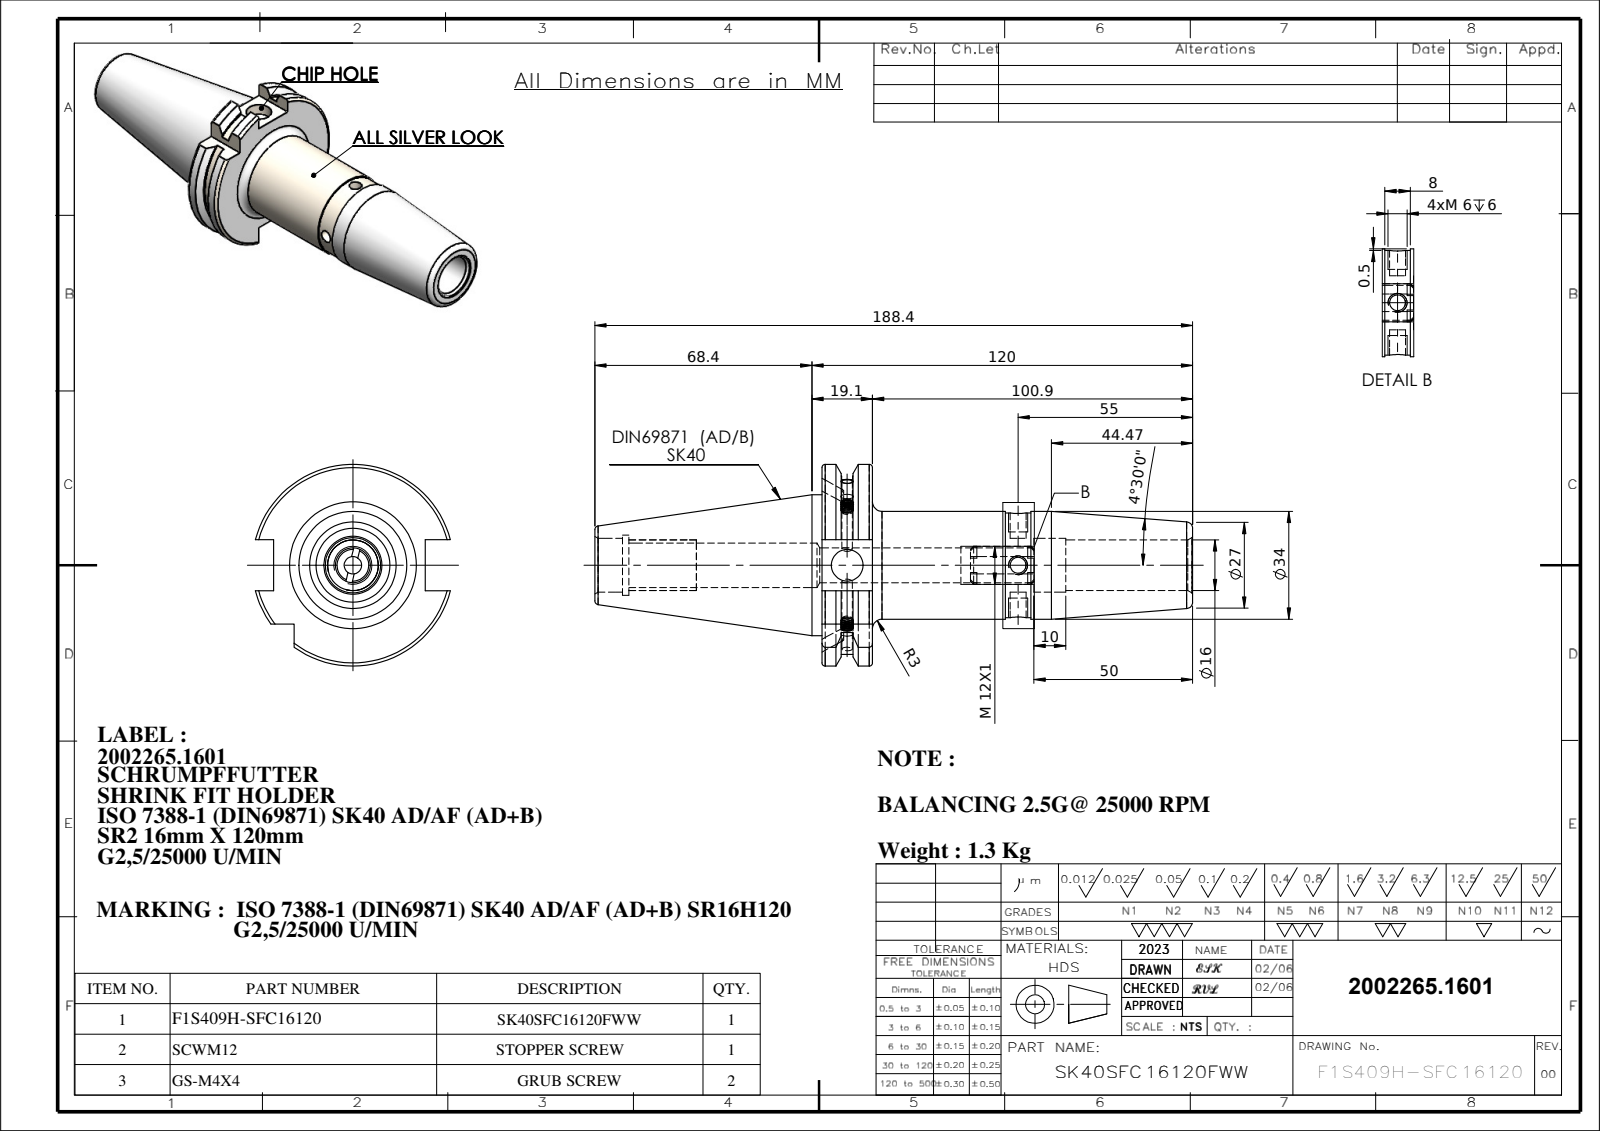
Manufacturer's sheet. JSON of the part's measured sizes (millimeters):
{"part_name": "GS-M4X4_DIN 913 - M4 x 4-N; 91406-SR216120; SCWM12; SK40SFC16120FWW", "step_written_by": "SolidWorks 2018 (CONFIG_CONTROL_DESIGN)", "units": "millimeters", "bodies": {"solids": 4, "faces": 238, "planar": 70, "cylindrical": 70, "other": 98}, "overall_size": [188.4, 63.55, 61.48], "volume_mm3": 168864, "surface_area_mm2": 37341, "round_holes": [[5, 2], [3.3, 1], [5.5, 1], [10, 1], [11, 1], [14, 1], [15.99, 1], [16.99, 1], [17, 1], [19, 1]], "round_bosses_or_shafts": [[4, 2], [44.45, 1], [34, 1], [33, 1], [12, 1]], "partial_cylinders_radius": [[28.12, 1], [31.77, 1]], "face_to_face_distances": [15.9, 16.1, 47.8, 66.8, 50.9, 116.8, 100.9, 50, 60.9, 76.8], "hole_center_spacings": [53.85]}
